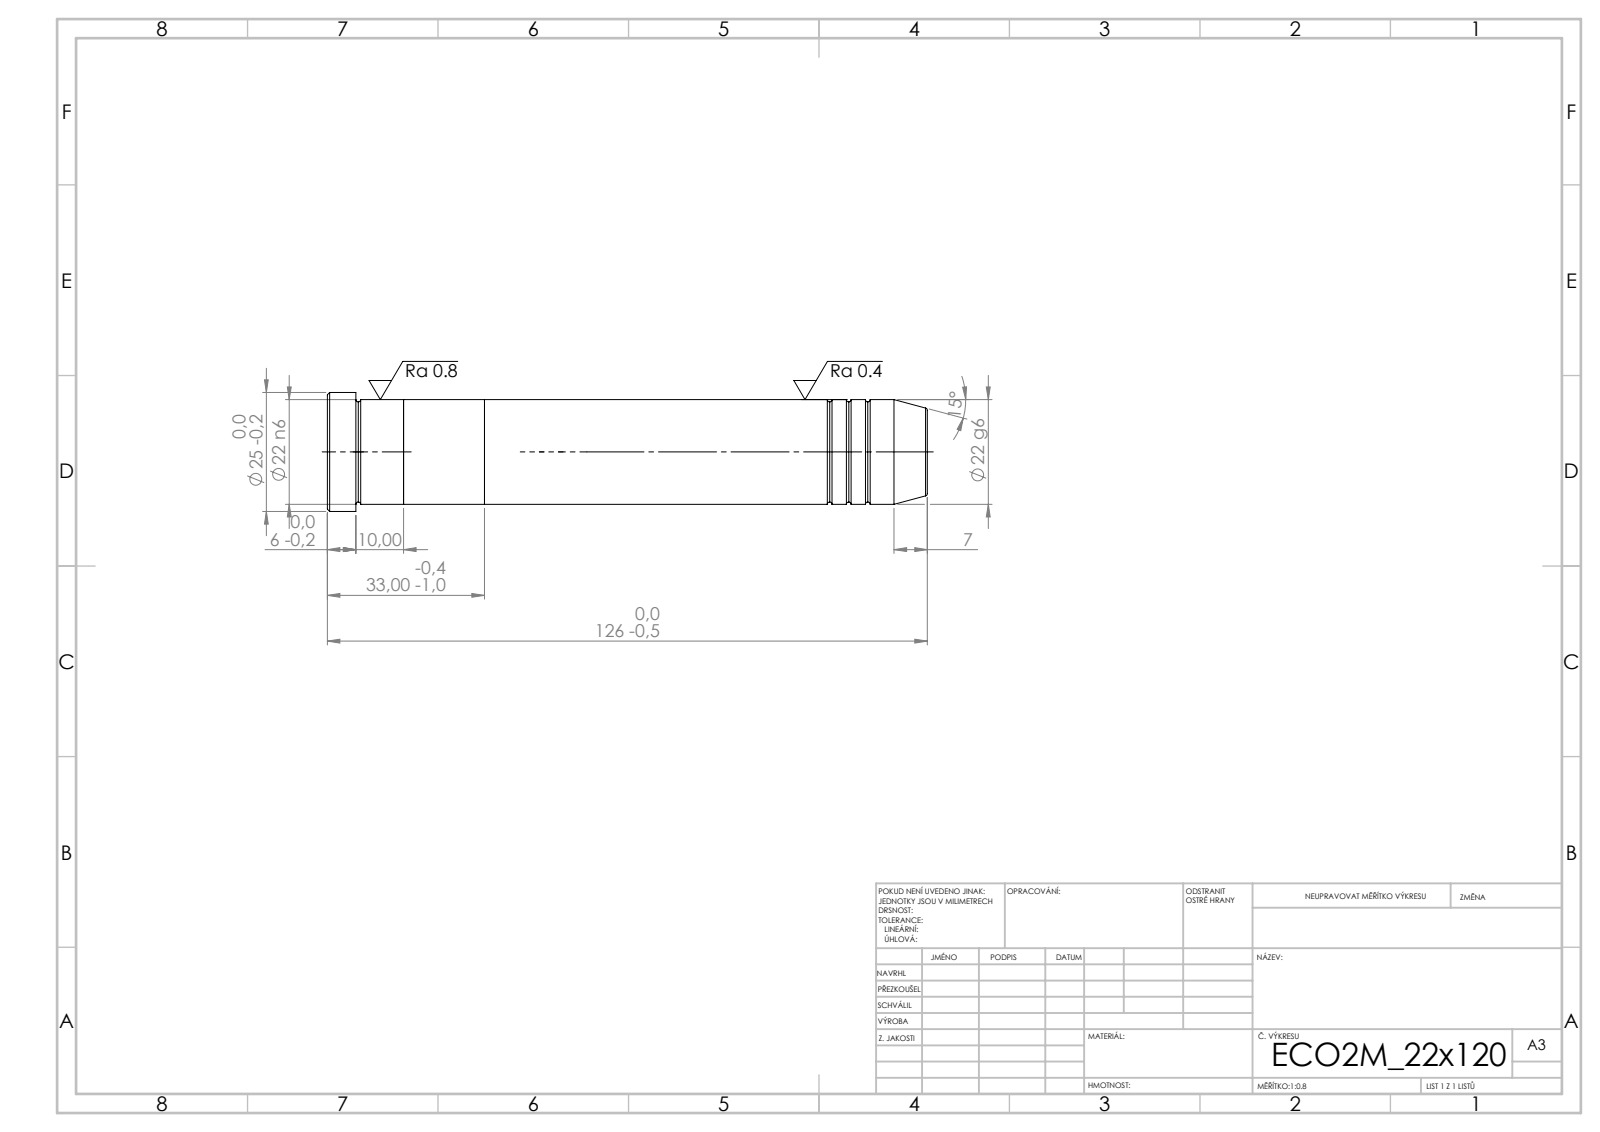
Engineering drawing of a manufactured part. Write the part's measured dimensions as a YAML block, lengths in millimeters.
step_written_by: "SolidWorks 2019 (CONFIG_CONTROL_DESIGN)"
units: millimeters
bodies: {solids: 3, faces: 43, planar: 7, cylindrical: 14, other: 22}
overall_size: [126, 25, 25]
volume: 48015
surface_area: 11238
round_bosses_or_shafts:
  - {diameter: 25, count: 1}
  - {diameter: 22, count: 1}
face_to_face_distances: [17, 33, 16, 93, 110, 126, 120, 27, 10, 6]
